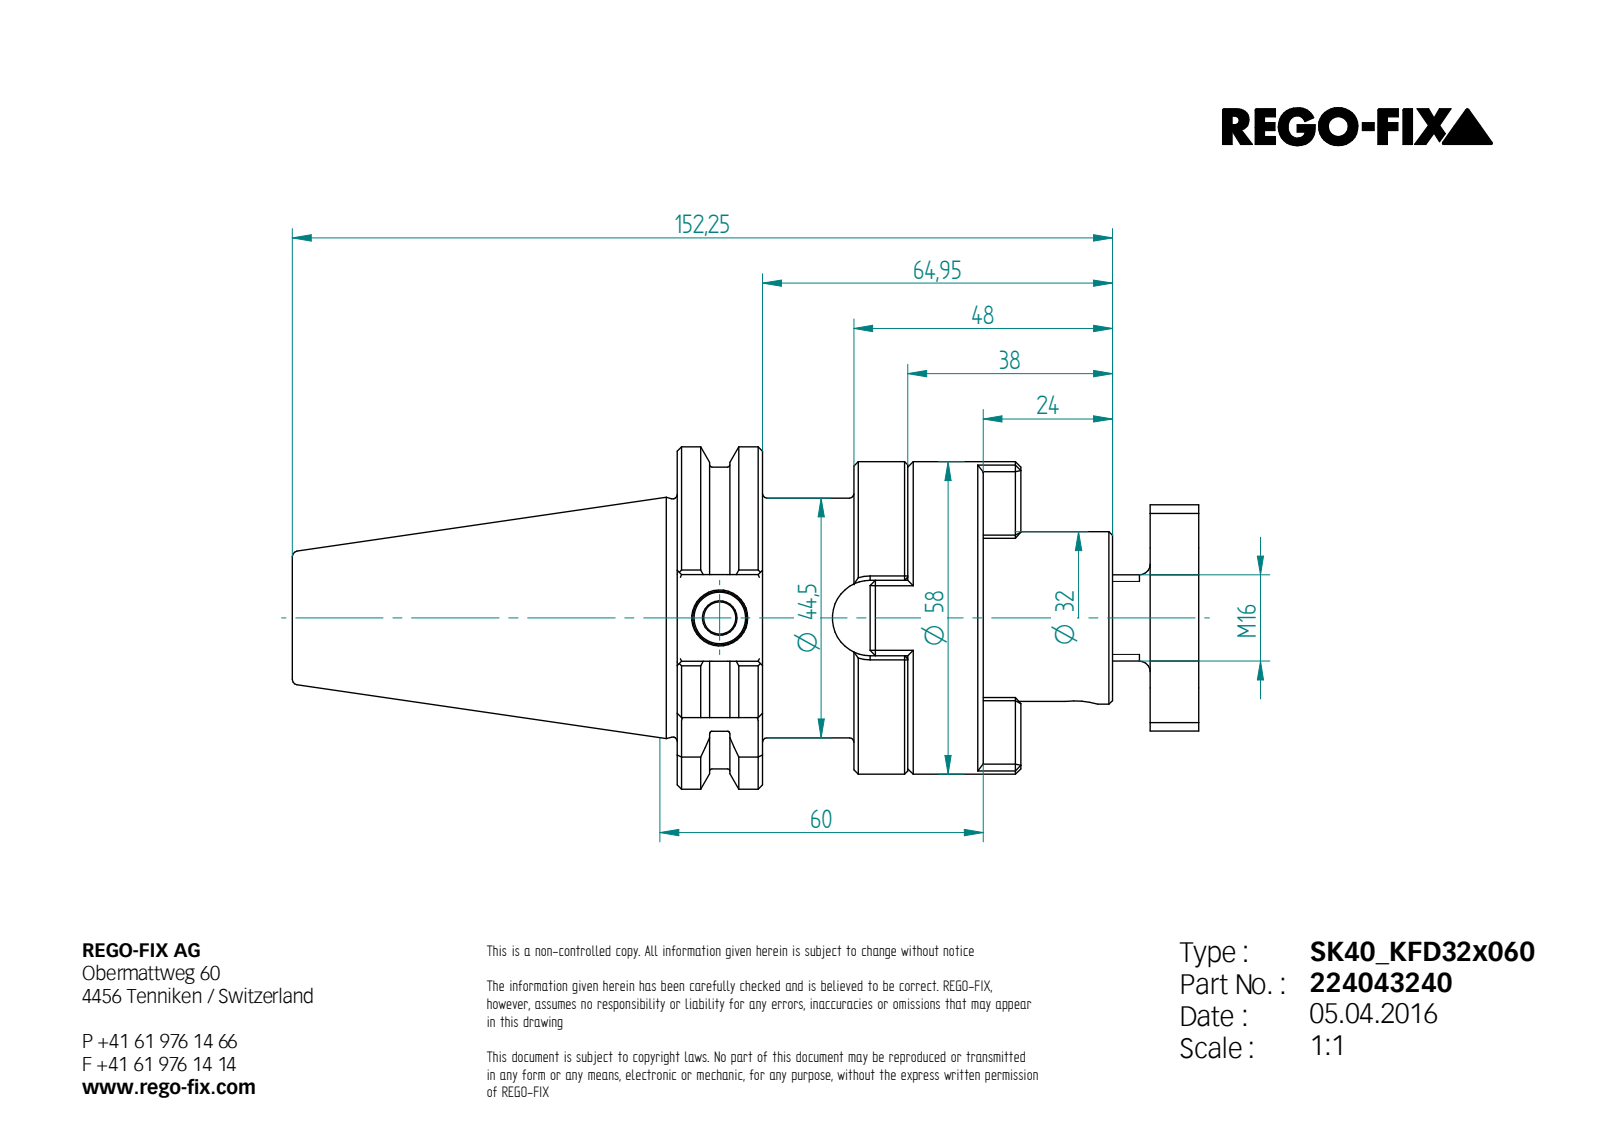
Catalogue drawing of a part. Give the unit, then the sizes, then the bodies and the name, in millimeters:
Units: millimetres
Overall size (bounding box): 168.25 × 63.55 × 61.01
Round holes (diameter × count): ⌀6 ×1, ⌀10 ×1, ⌀13.84 ×1, ⌀17 ×1, ⌀32 ×1
Round bosses / shafts (diameter × count): ⌀58 ×1, ⌀44.5 ×1, ⌀31.4 ×1, ⌀16 ×1
Partial cylindrical surfaces — rounded edges, fillets, slot ends (radius × count): R0.5 ×13, R5 ×4, R4 ×2, R7 ×1, R21 ×1, R28 ×1, R31.77 ×1
Main face-to-face distances: 14, 24, 40.95, 42.8, 56.8, 96.8, 54, 40, 15.85, 26.95
Volume: 212 553 mm³ · Surface area: 46 808 mm²
Bodies: 3 solids, 248 faces (132 planar, 49 cylindrical, 67 other)
STEP written by: Unknown (AUTOMOTIVE_DESIGN)
